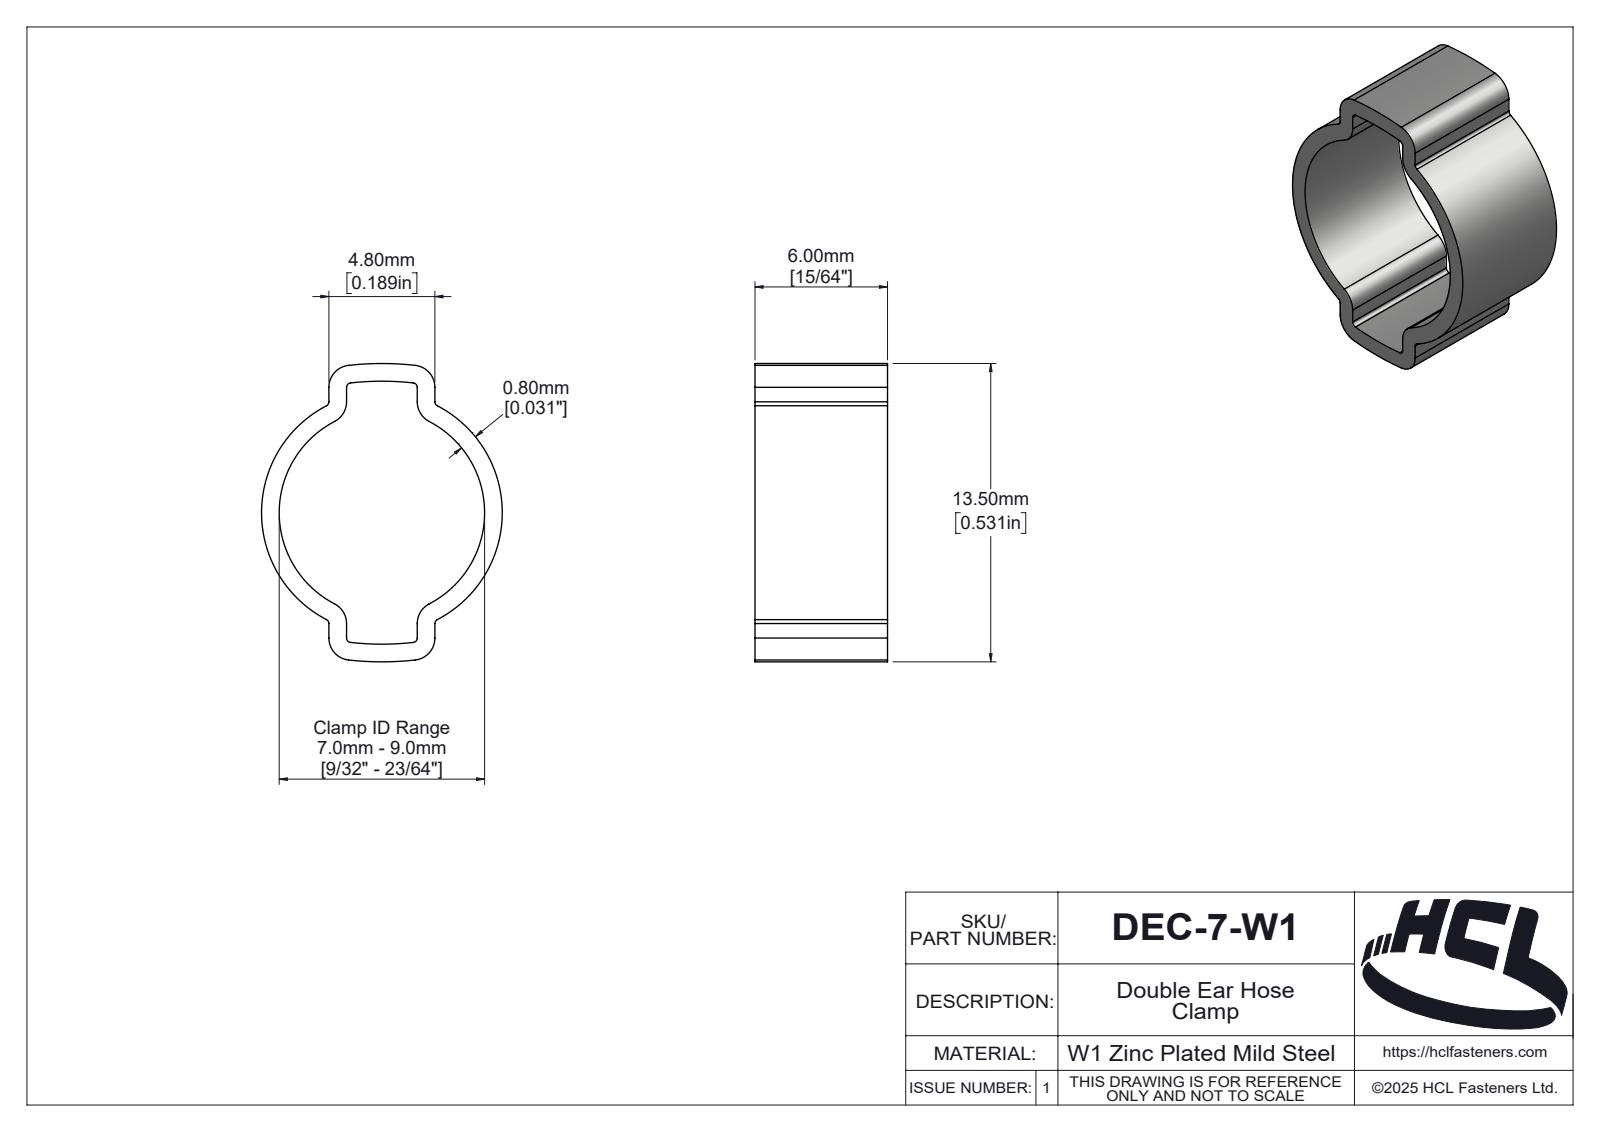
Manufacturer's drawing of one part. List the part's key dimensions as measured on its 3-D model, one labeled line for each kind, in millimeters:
Part name (STEP PRODUCT): DEC-7-W1
STEP written by: SolidWorks 2025 (AUTOMOTIVE_DESIGN)
Units: millimetres
Bodies: 1 solid, 137 faces (12 planar, 76 cylindrical, 49 other)
Overall size (bounding box): 13.5 × 10.9 × 6
Volume: 176 mm³ · Surface area: 502 mm²
Partial cylindrical surfaces — rounded edges, fillets, slot ends (radius × count): R0.2 ×8, R1 ×8, R12.85 ×2, R13.65 ×2, R0.13 ×1, R0.54 ×1, R0.67 ×1, R0.71 ×1
Main face-to-face distances: 6, 0.8, 4, 4.8, 3.2, 2.22, 1.42, 1.78, 2.58, 2.32
